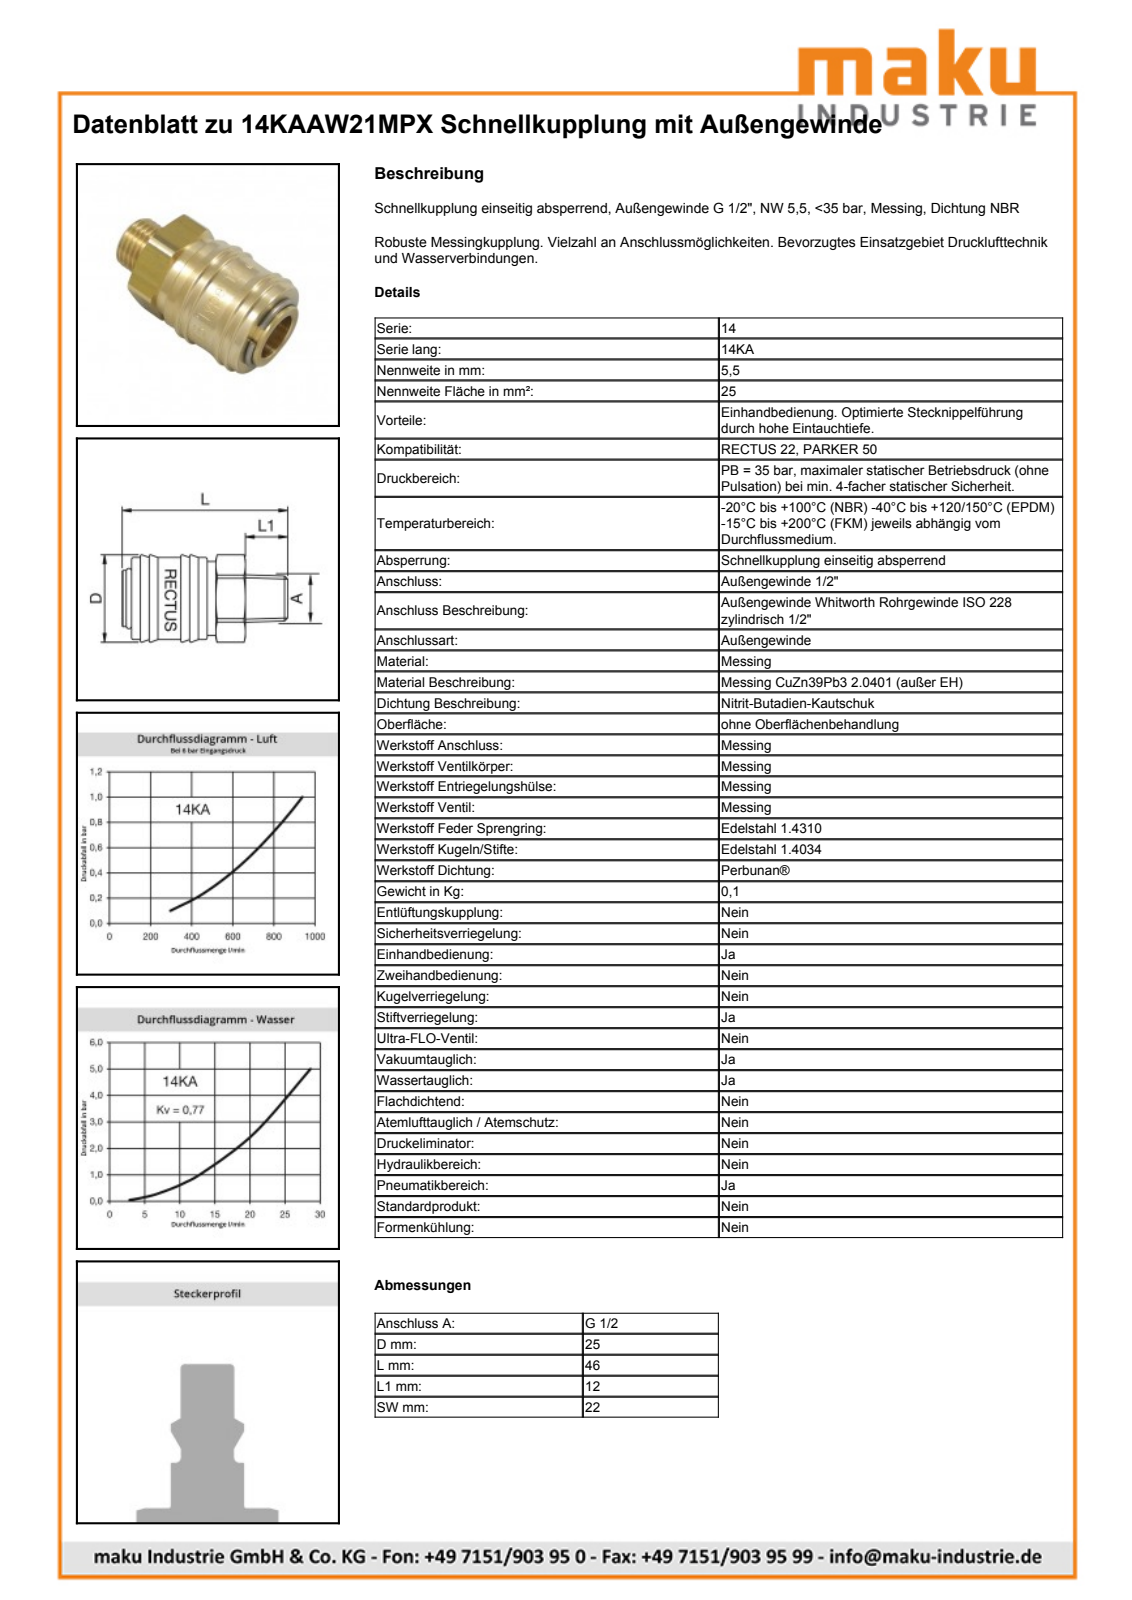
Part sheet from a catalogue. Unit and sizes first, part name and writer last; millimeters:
Units: millimetres
Overall size (bounding box): 46.6 × 24.8 × 24.8
Round holes (diameter × count): ⌀16.1 ×1, ⌀17.15 ×1, ⌀21.1 ×1
Round bosses / shafts (diameter × count): ⌀23.3 ×1, ⌀21 ×1, ⌀20.95 ×1, ⌀18 ×1, ⌀16.65 ×1, ⌀15.95 ×1, ⌀14.95 ×1
Partial cylindrical surfaces — rounded edges, fillets, slot ends (radius × count): R6.64 ×1, R11.55 ×1, R12.4 ×1
Main face-to-face distances: 22, 43.95, 2.65, 46.6, 23.5, 20.85, 23.1, 2.1, 13, 10.35
Volume: 16 121 mm³ · Surface area: 7 861 mm²
Bodies: 3 solids, 493 faces (210 planar, 56 cylindrical, 227 other)
Part name (STEP PRODUCT): D113527
STEP written by: Autodesk Inventor 2013 (AUTOMOTIVE_DESIGN)
